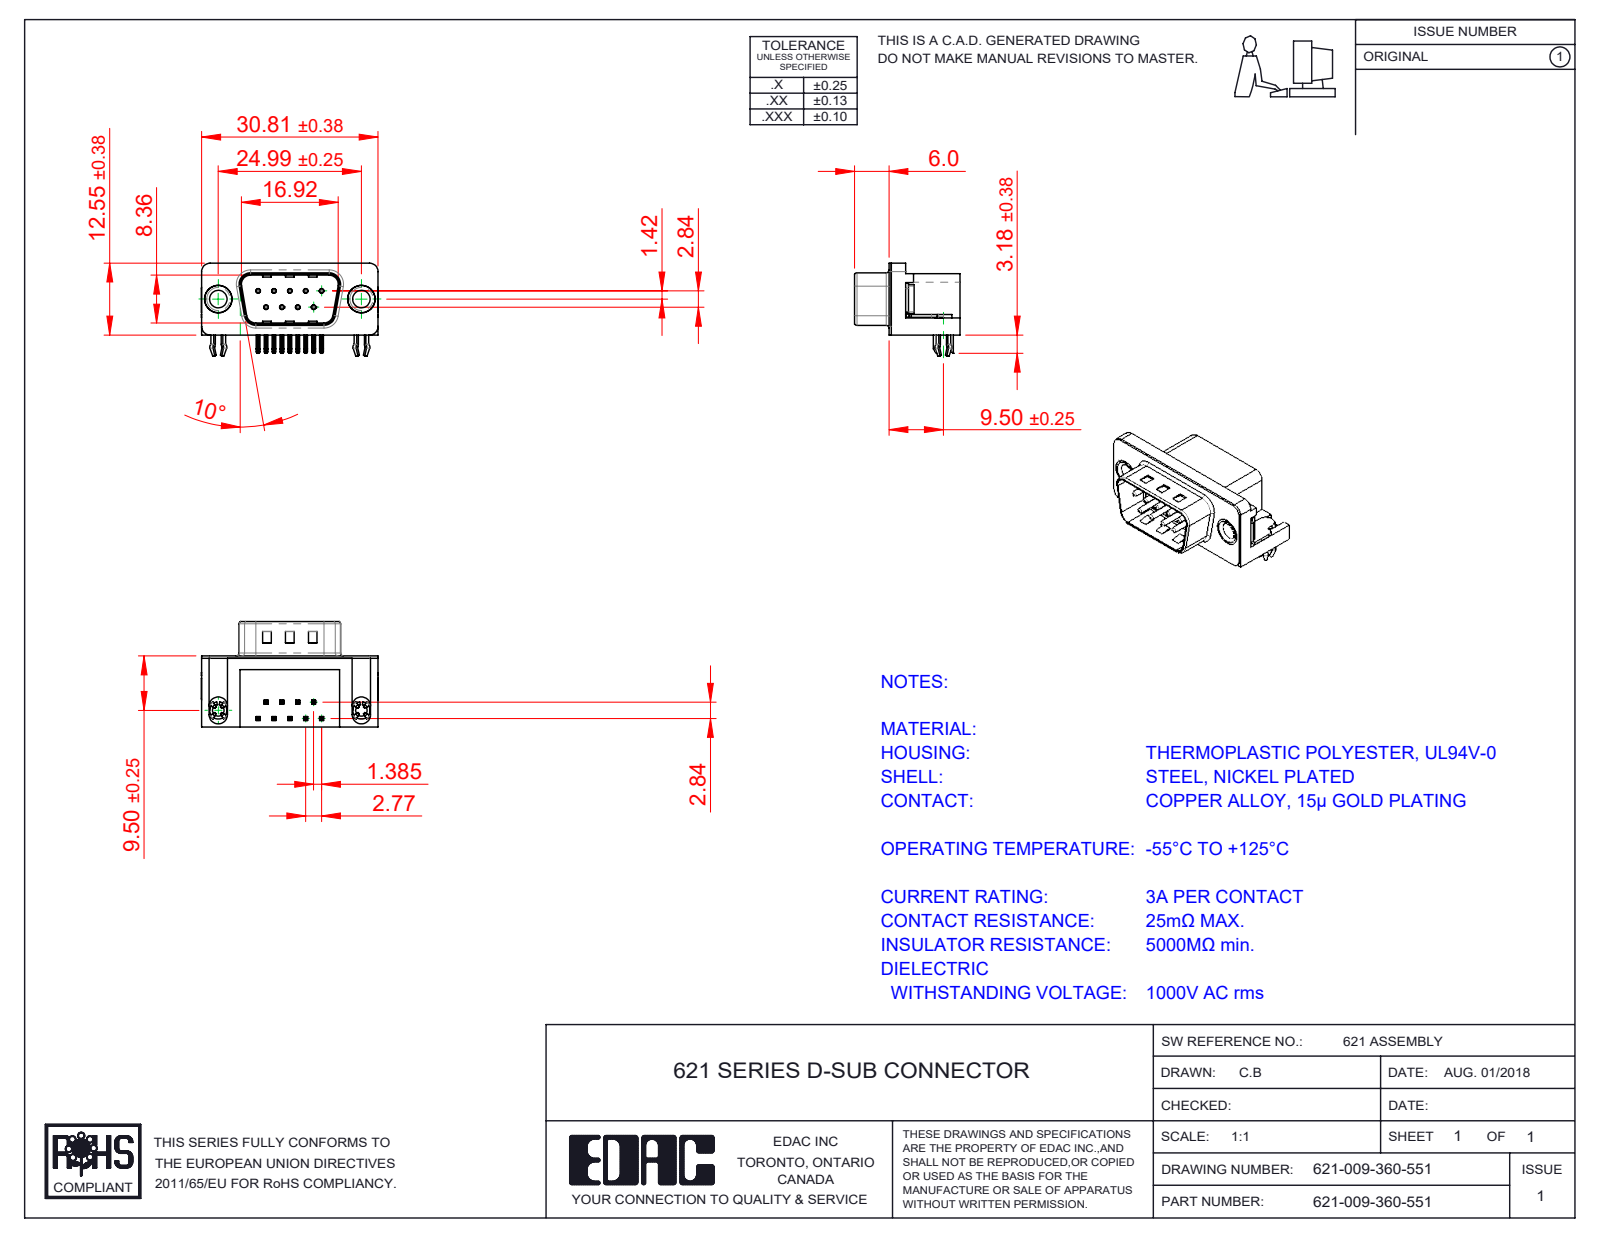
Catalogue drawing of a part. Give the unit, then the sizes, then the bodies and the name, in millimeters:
Units: millimetres
Overall size (bounding box): 30.89 × 18.4 × 15.73
Round holes (diameter × count): ⌀0.35 ×9, ⌀0.8 ×9, ⌀2.26 ×2, ⌀3.05 ×2, ⌀4 ×2, ⌀4.8 ×2, ⌀5 ×2
Round bosses / shafts (diameter × count): ⌀0.75 ×9, ⌀4.9 ×2, ⌀4.75 ×2, ⌀3.85 ×2, ⌀3.26 ×2
Partial cylindrical surfaces — rounded edges, fillets, slot ends (radius × count): R0.25 ×44, R0.12 ×18, R1 ×16, R0.5 ×9, R1.5 ×8, R1.6 ×8, R0.9 ×4, R2 ×4
Main face-to-face distances: 0.4, 12, 12.4, 10.35, 2.9, 9.5, 2.5, 0.5, 2.1, 0.35
Hole centre spacings: 3.16, 2.77, 5.54, 5.03, 5.04, 8.31, 7.48, 7.49
Volume: 3 245 mm³ · Surface area: 4 477 mm²
Bodies: 15 solids, 981 faces (573 planar, 309 cylindrical, 99 other)
Part name (STEP PRODUCT): 621 Contact Bottom; 621 Shell_9 Socket; 621 Housing_9 Socket; 621 Contact Top (+3 more)
STEP written by: SolidWorks 2016 (CONFIG_CONTROL_DESIGN)
